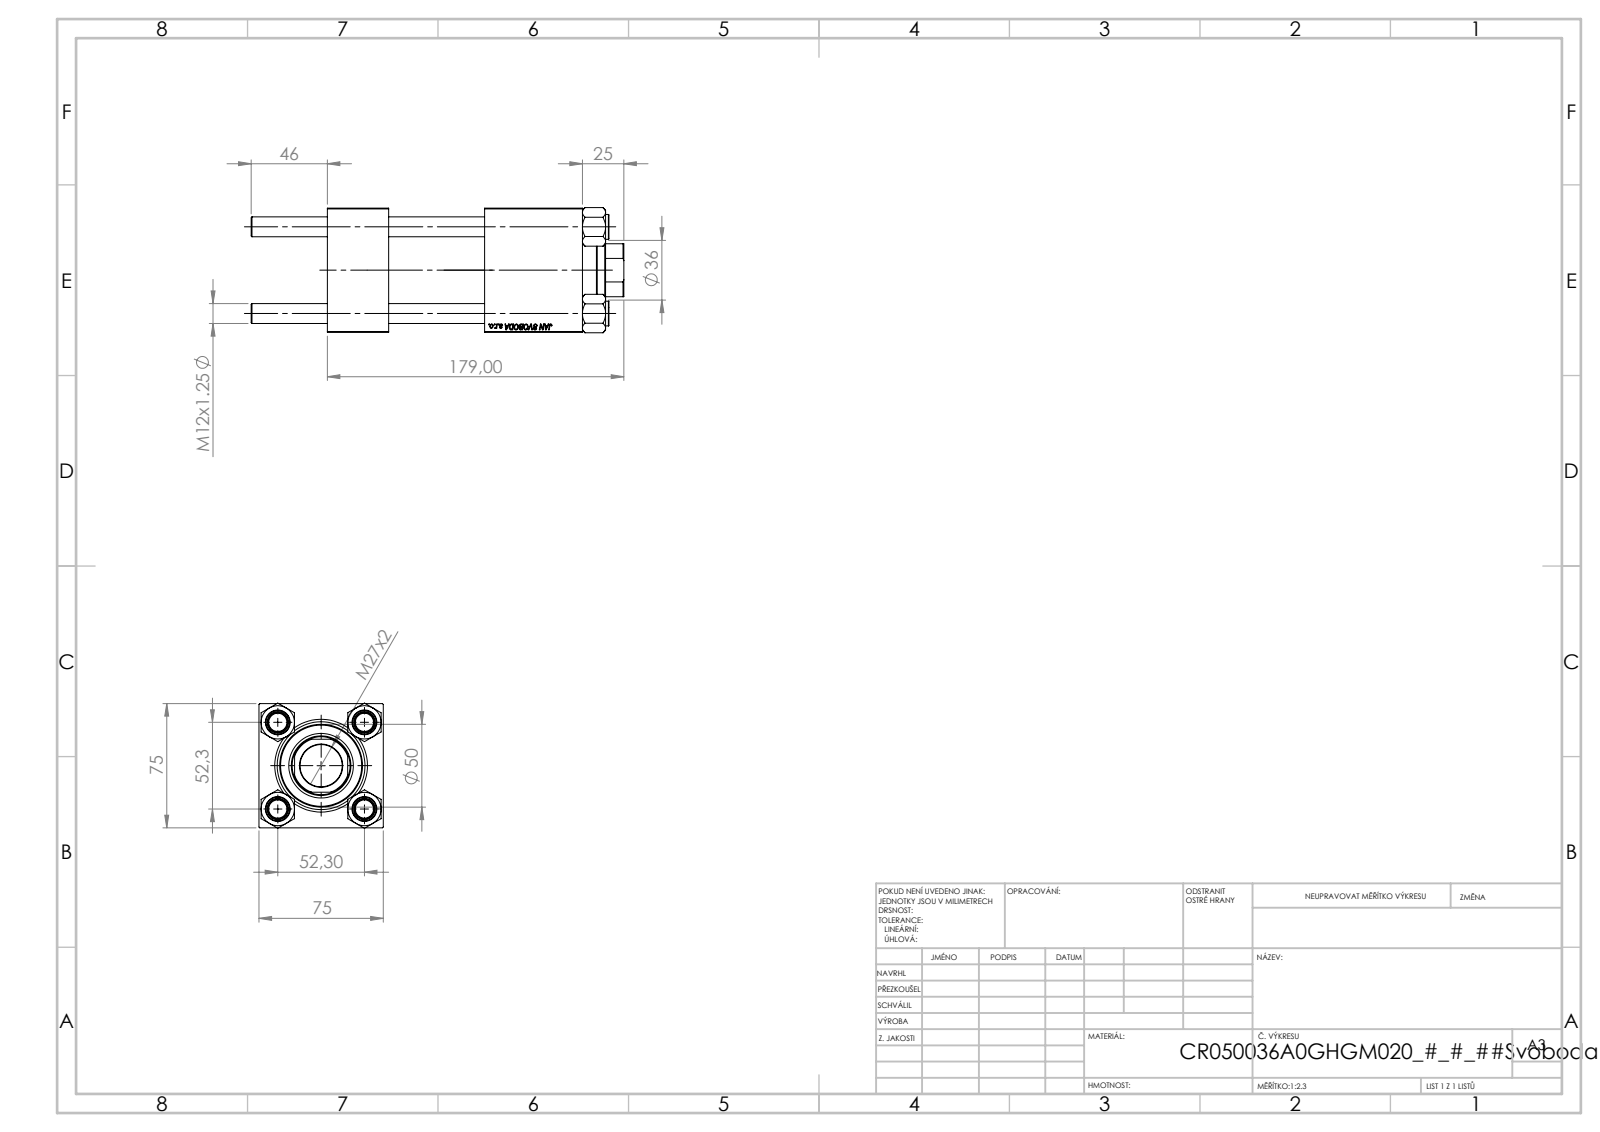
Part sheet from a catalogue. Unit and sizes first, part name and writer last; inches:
Units: inches
Overall size (bounding box): 8.858 × 2.974 × 2.953
Round holes (diameter × count): ⌀0.472 ×4, ⌀0.276 ×2, ⌀0.825 ×2, ⌀1.181 ×2, ⌀1.004 ×1, ⌀1.417 ×1, ⌀1.535 ×1, ⌀1.614 ×1, ⌀2.087 ×1
Round bosses / shafts (diameter × count): ⌀0.591 ×4, ⌀2.205 ×1, ⌀1.969 ×1
Partial cylindrical surfaces — rounded edges, fillets, slot ends (radius × count): R0.689 ×1
Main face-to-face distances: 2.953, 1.457, 3.74, 6.063, 4.606, 2.283, 2.323, 4.933, 3.476, 1.193
Hole centre spacings: 1.456, 2.059, 2.912, 3.681
Volume: 43.89 in³ · Surface area: 266.5 in²
Bodies: 11 solids, 1134 faces (520 planar, 78 cylindrical, 536 other)
Part name (STEP PRODUCT): CR025_012_A_0_G_A_G_M_020_+#_##_TYCINKA; V215CR_VCP; NUT_M5; V215_VC_A (+1 more)
STEP written by: SolidWorks 2019 (CONFIG_CONTROL_DESIGN)
